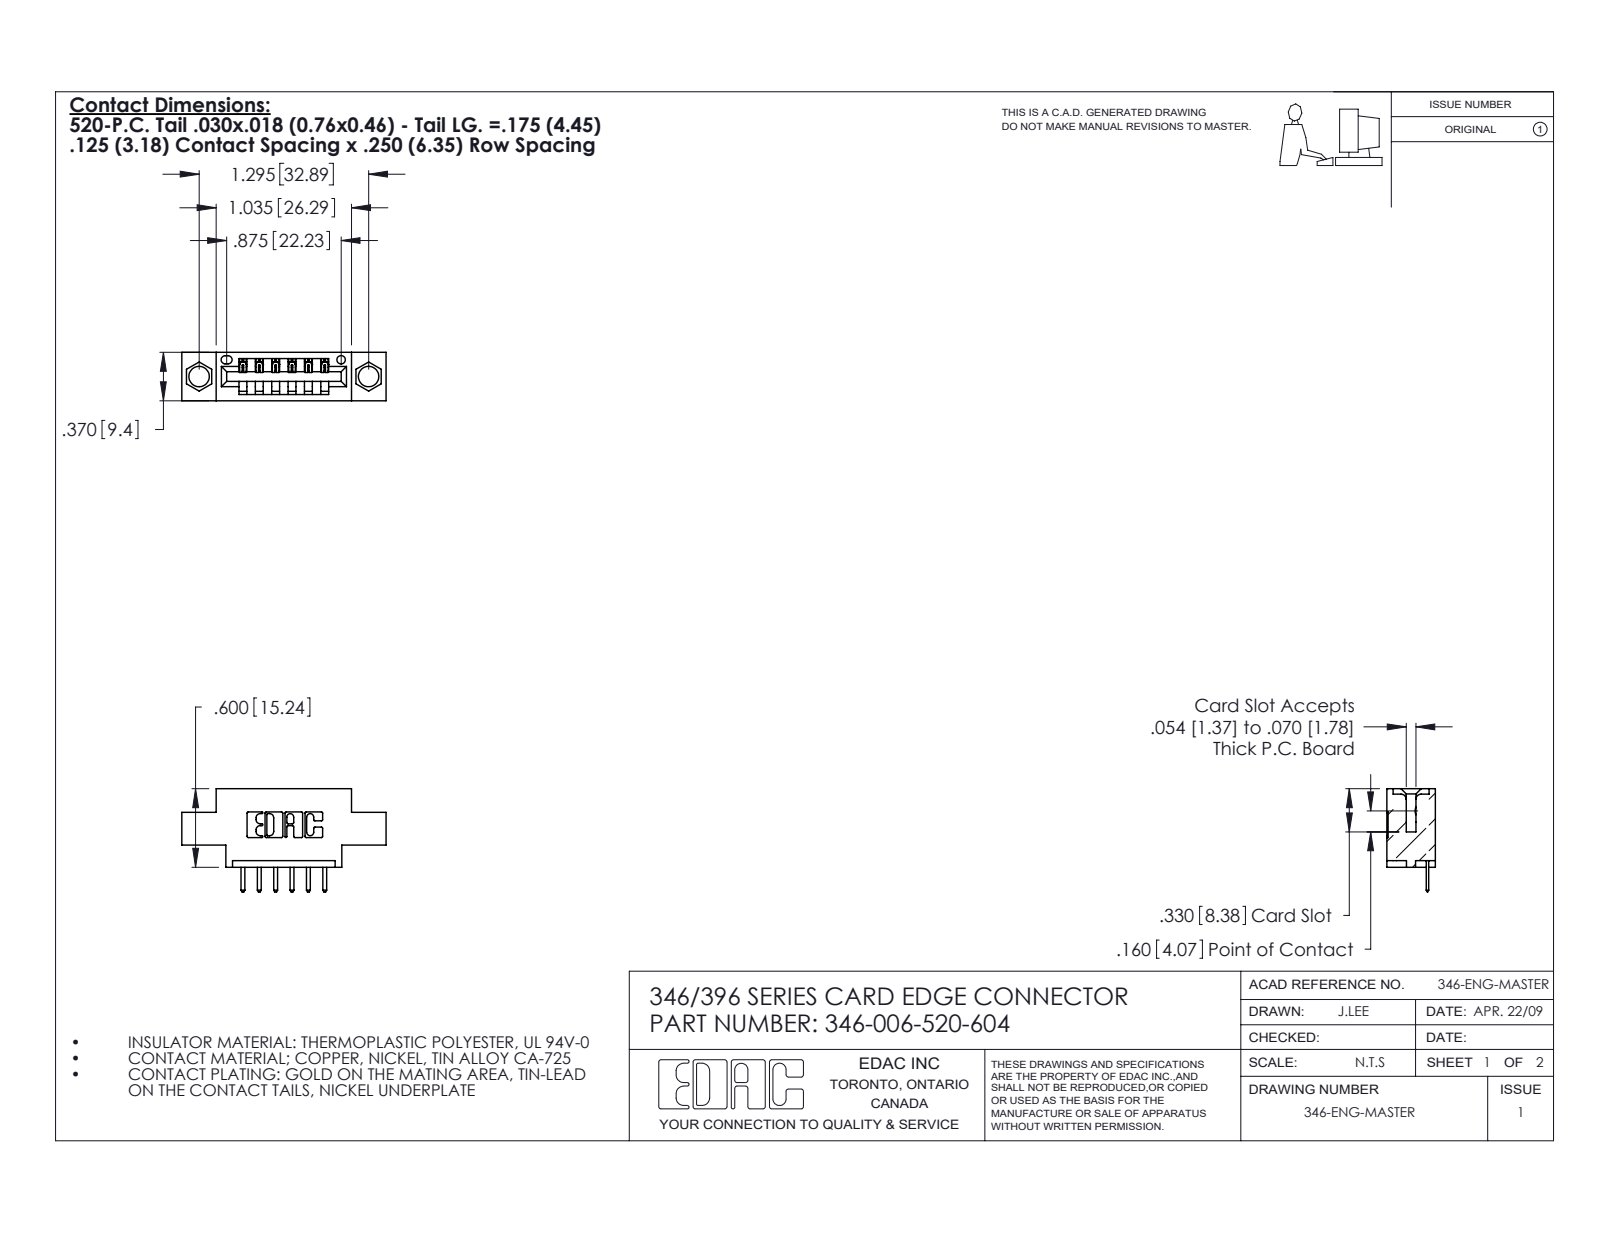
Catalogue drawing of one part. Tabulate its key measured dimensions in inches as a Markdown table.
| quantity | value |
| --- | --- |
| part name | 345-292-001_345-293-120; 346-006-520-604; 346 Part_0.170 Offset - 0.156 Dia-TH |
| STEP written by | SolidWorks 2020 (CONFIG_CONTROL_DESIGN) |
| units | inches |
| bodies | 7 solids, 512 faces (346 planar, 166 cylindrical, 0 other) |
| overall size | 1.56 × 0.788 × 0.37 |
| volume | 0.199 in³ |
| surface area | 5.634 in² |
| round holes (diameter × count) | 0.156 × 2, 0.064 × 1 |
| partial cylindrical surfaces (radius × count) | 0.01 × 22, 0.01 × 14, 0.006 × 12, 0.007 × 6, 0.031 × 6, 0.026 × 3, 0.031 × 2, 0.04 × 2 |
| main face-to-face distances | 0.25, 0.37, 0.048, 0.322, 0.222, 0.148, 0.1, 0.174, 0.125, 0.185 |
| hole center spacings | 0.246, 1.092, 1.295 |
